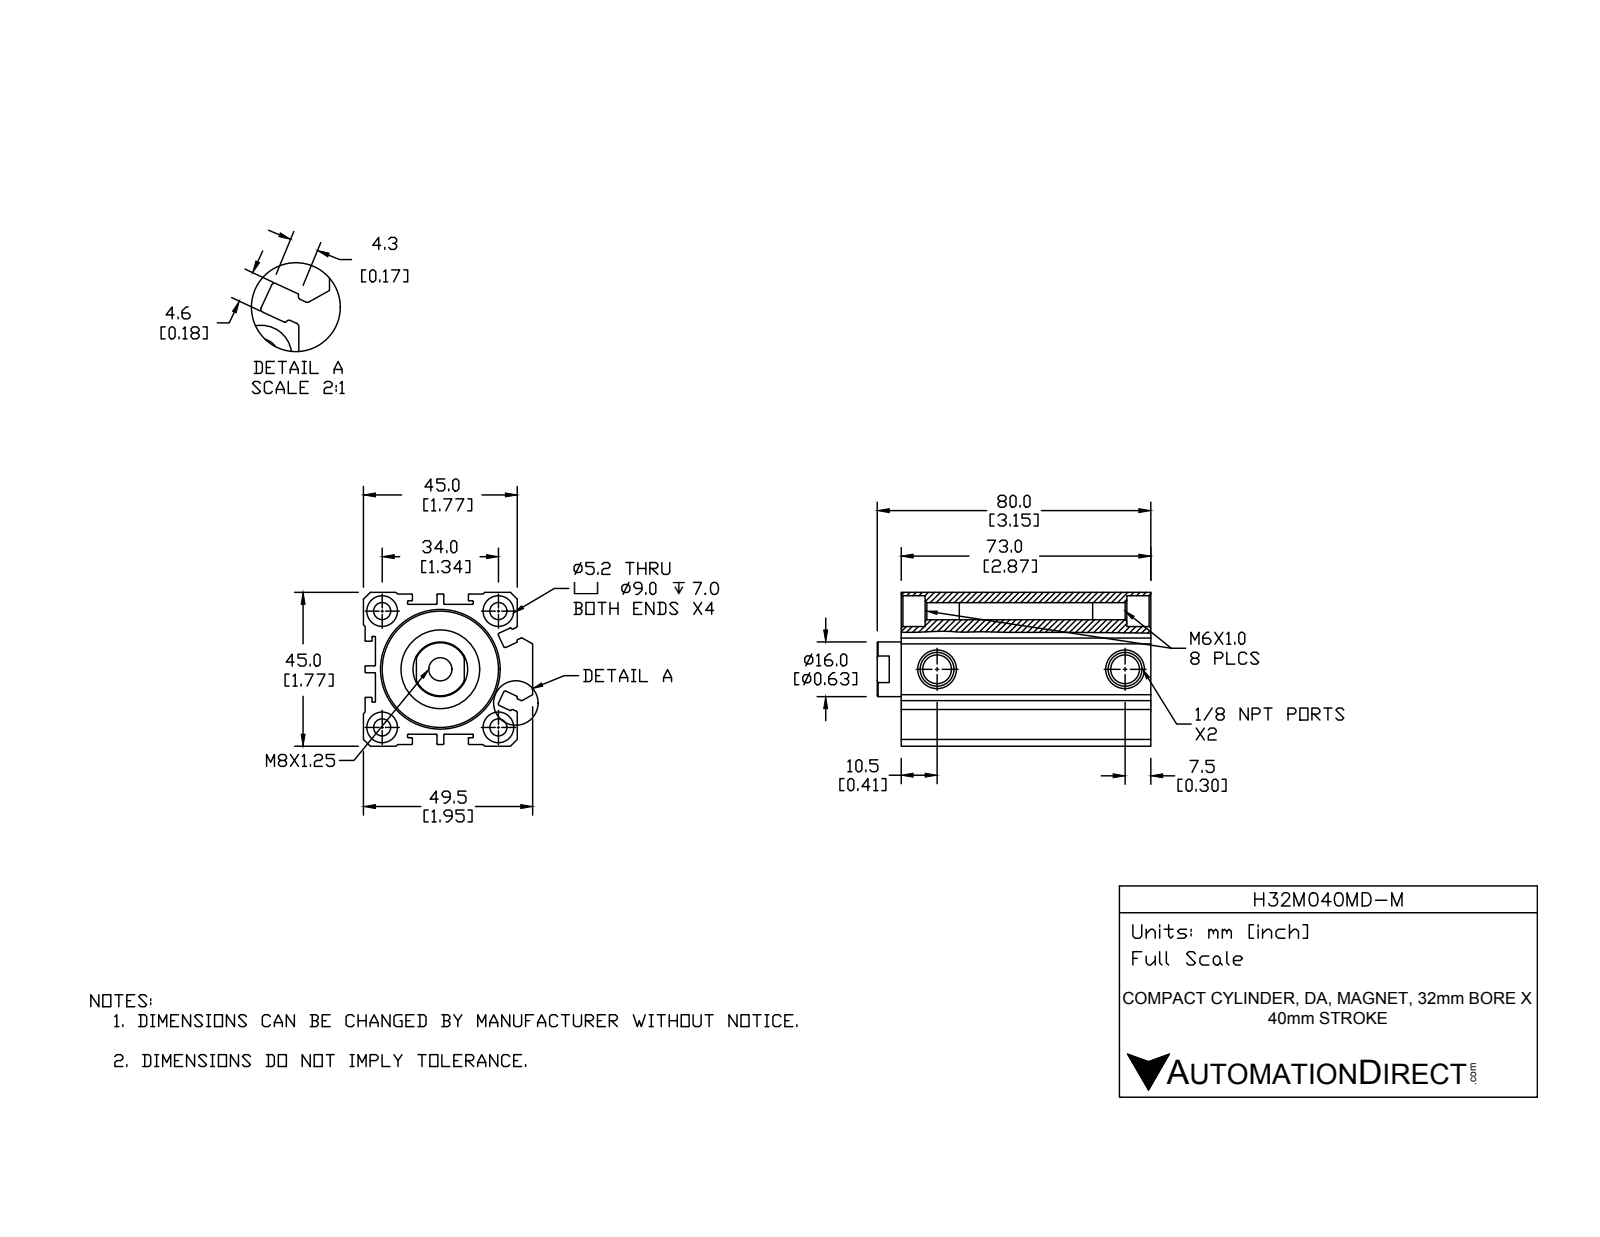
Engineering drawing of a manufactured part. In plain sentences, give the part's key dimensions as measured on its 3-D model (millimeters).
The part is named "H32M040MD-M; H32M040MD-M-PISTON; H32M040MD-M-BODY". Its 3-D file was written by "SolidWorks 2015 (CONFIG_CONTROL_DESIGN)". It is 2 solids with 255 faces: 99 planar, 103 cylindrical and 53 other. Overall it measures 80 by 49.5 by 45 millimeters. Its volume is 100 537 cubic millimeters and its surface area 42 830 square millimeters. Round holes: 4 of diameter 5, 4 of diameter 9, 2 of diameter 8.43, 1 of diameter 6.8, 1 of diameter 16, 1 of diameter 23, 1 of diameter 28, 1 of diameter 32, 1 of diameter 34. Round bosses or shafts: 1 of diameter 20. Partial cylindrical surfaces (rounded edges, fillets, slot ends): 40 of radius 0.2, 12 of radius 0.5. The main face-to-face distances are 3.5, 41.5, 3, 45, 0.5, 44.5, 4.5, 41, 38, 21. The hole center spacings are 24.04, 34, 48.08, 55.
